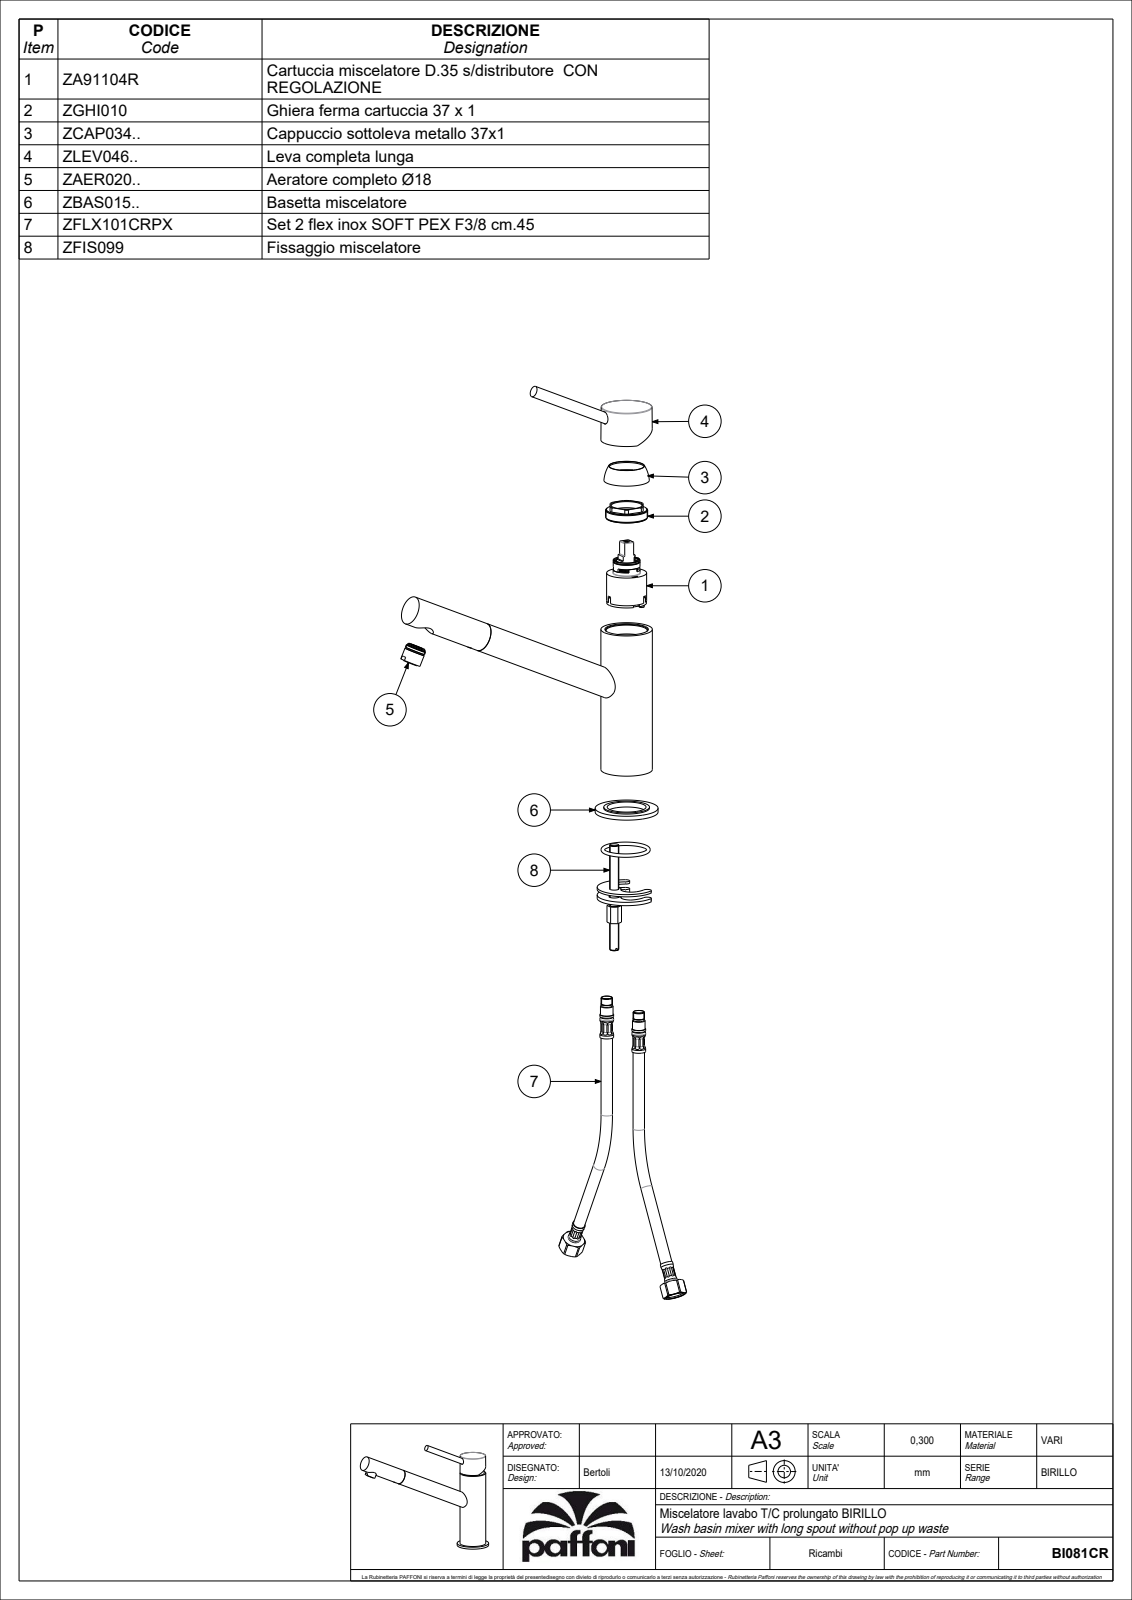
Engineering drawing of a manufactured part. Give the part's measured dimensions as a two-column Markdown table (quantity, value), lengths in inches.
| quantity | value |
| --- | --- |
| part name | BI081CR |
| STEP written by | CREO PARAMETRIC BY PTC INC, 2020044 (CONFIG_CONTROL_DESIGN) |
| units | inches |
| bodies | 1 solid, 1087 faces (606 planar, 256 cylindrical, 225 other) |
| overall size | 9.89 × 7.592 × 2.165 |
| volume | 17.9 in³ |
| surface area | 126 in² |
| round holes (diameter × count) | 0.433 × 3, 0.157 × 2, 0.256 × 2, 0.354 × 2, 0.13 × 1, 0.177 × 1, 0.197 × 1, 0.217 × 1, 0.268 × 1, 0.394 × 1, 0.61 × 1, 0.724 × 1 |
| round bosses / shafts (diameter × count) | 2.165 × 1, 1.772 × 1, 1.575 × 1, 1.457 × 1, 1.378 × 1, 1.37 × 1, 1.268 × 1, 0.984 × 1 |
| partial cylindrical surfaces (radius × count) | 0.02 × 51, 0.006 × 11, 0.012 × 4, 0.039 × 2, 0.041 × 1, 0.118 × 1, 0.197 × 1, 0.276 × 1 |
| main face-to-face distances | 1.043, 5.201, 0.138, 0.177, 0.217, 4.783, 4.106, 3.969, 0.906, 3.063 |
| hole center spacings | 0.139, 0.317, 0.344, 0.432, 0.552, 0.626, 0.492, 0.591 |
